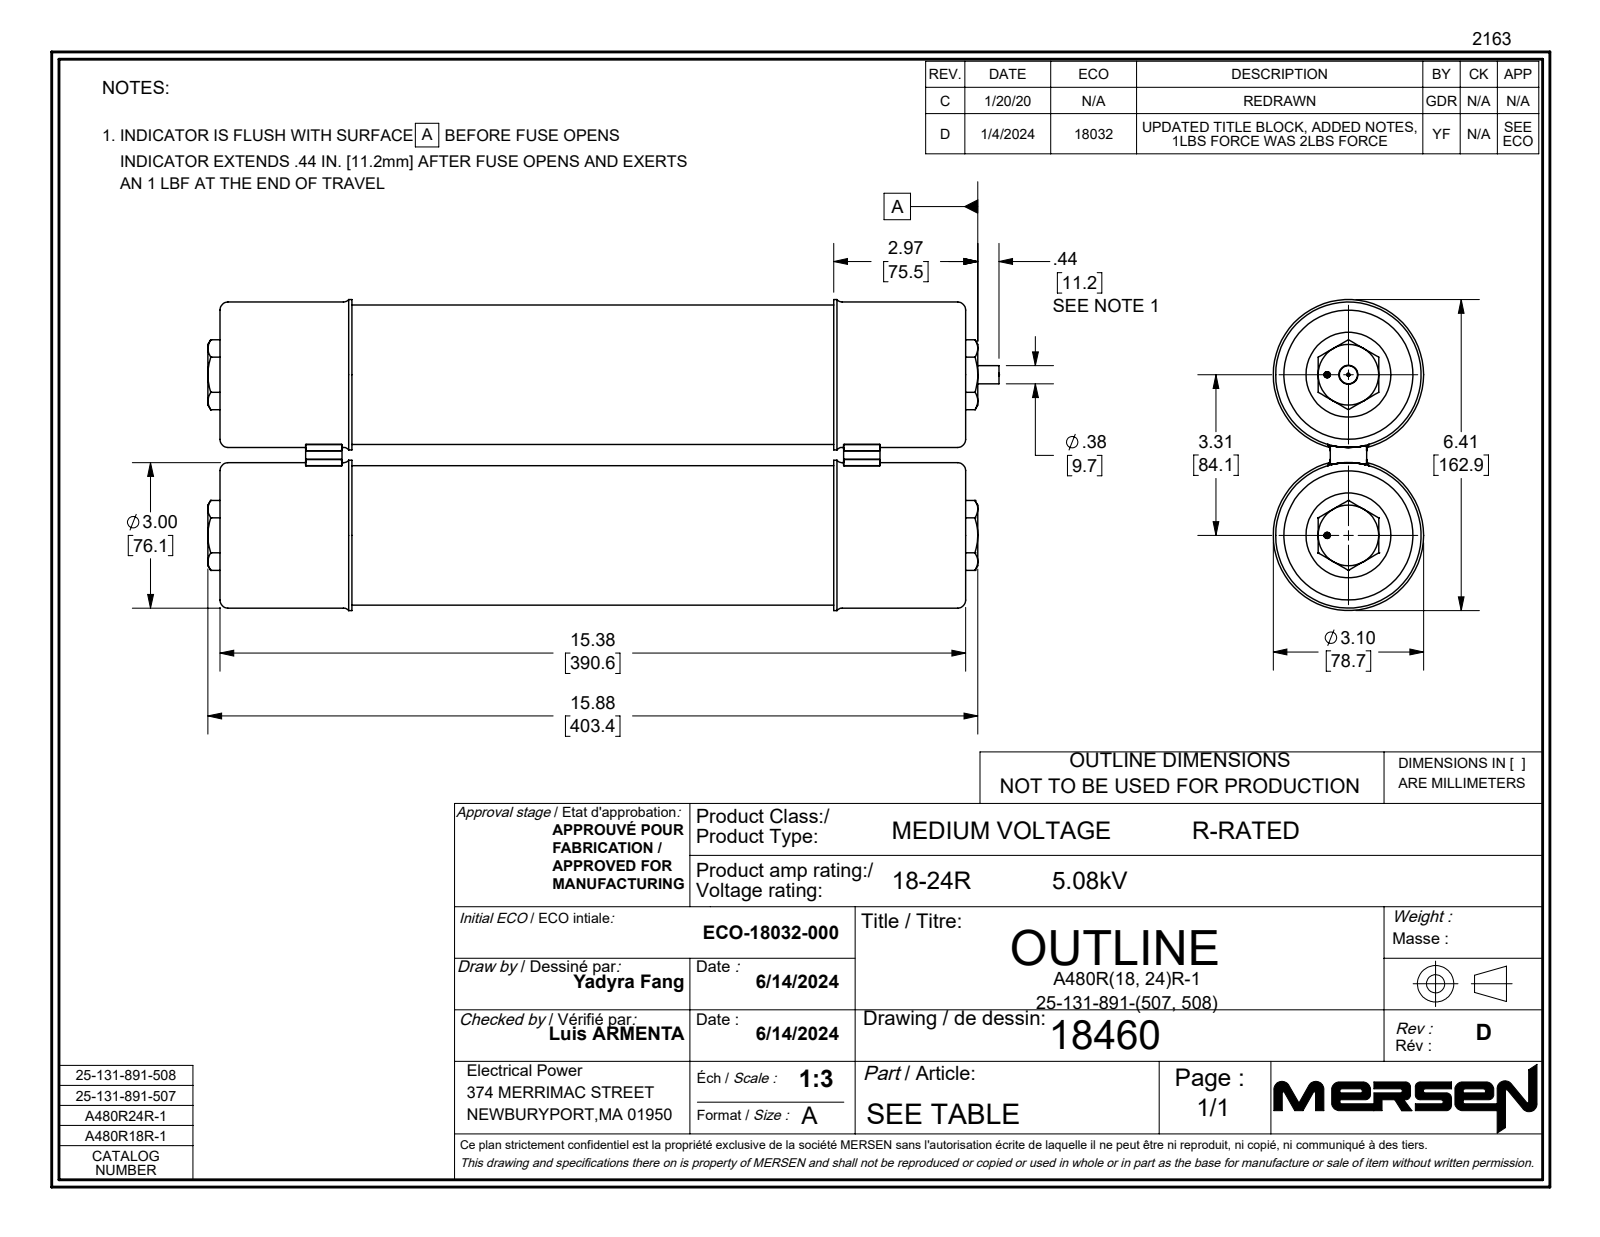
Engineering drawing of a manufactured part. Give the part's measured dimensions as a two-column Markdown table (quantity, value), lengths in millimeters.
| quantity | value |
| --- | --- |
| part name | 18460 |
| STEP written by | SolidWorks 2021 (AUTOMOTIVE_DESIGN) |
| units | millimeters |
| bodies | 29 solids, 721 faces (241 planar, 259 cylindrical, 221 other) |
| overall size | 403.4 × 162.9 × 78.7 |
| volume | 701 500 mm³ |
| surface area | 529 300 mm² |
| round holes (diameter × count) | 1.8 × 2, 3.2 × 2, 23 × 2, 66.7 × 2, 73.4 × 2, 76.1 × 2, 0.5 × 1, 1.6 × 1, 3.7 × 1, 4.8 × 1, 9.9 × 1, 11.8 × 1 |
| round bosses / shafts (diameter × count) | 78.7 × 2, 73 × 2, 31.8 × 2, 19.8 × 2, 3.2 × 2, 3.2 × 2, 22.9 × 1, 22.2 × 1 |
| partial cylindrical surfaces (radius × count) | 101.6 × 5, 0.8 × 4, 4.7 × 4, 38.1 × 2 |
| main face-to-face distances | 1.4, 386.1, 8, 9.3, 394.1, 395.4, 10.2, 393.2, 2.3, 385.2 |
| hole center spacings | 11.1, 84.1, 84.9 |
